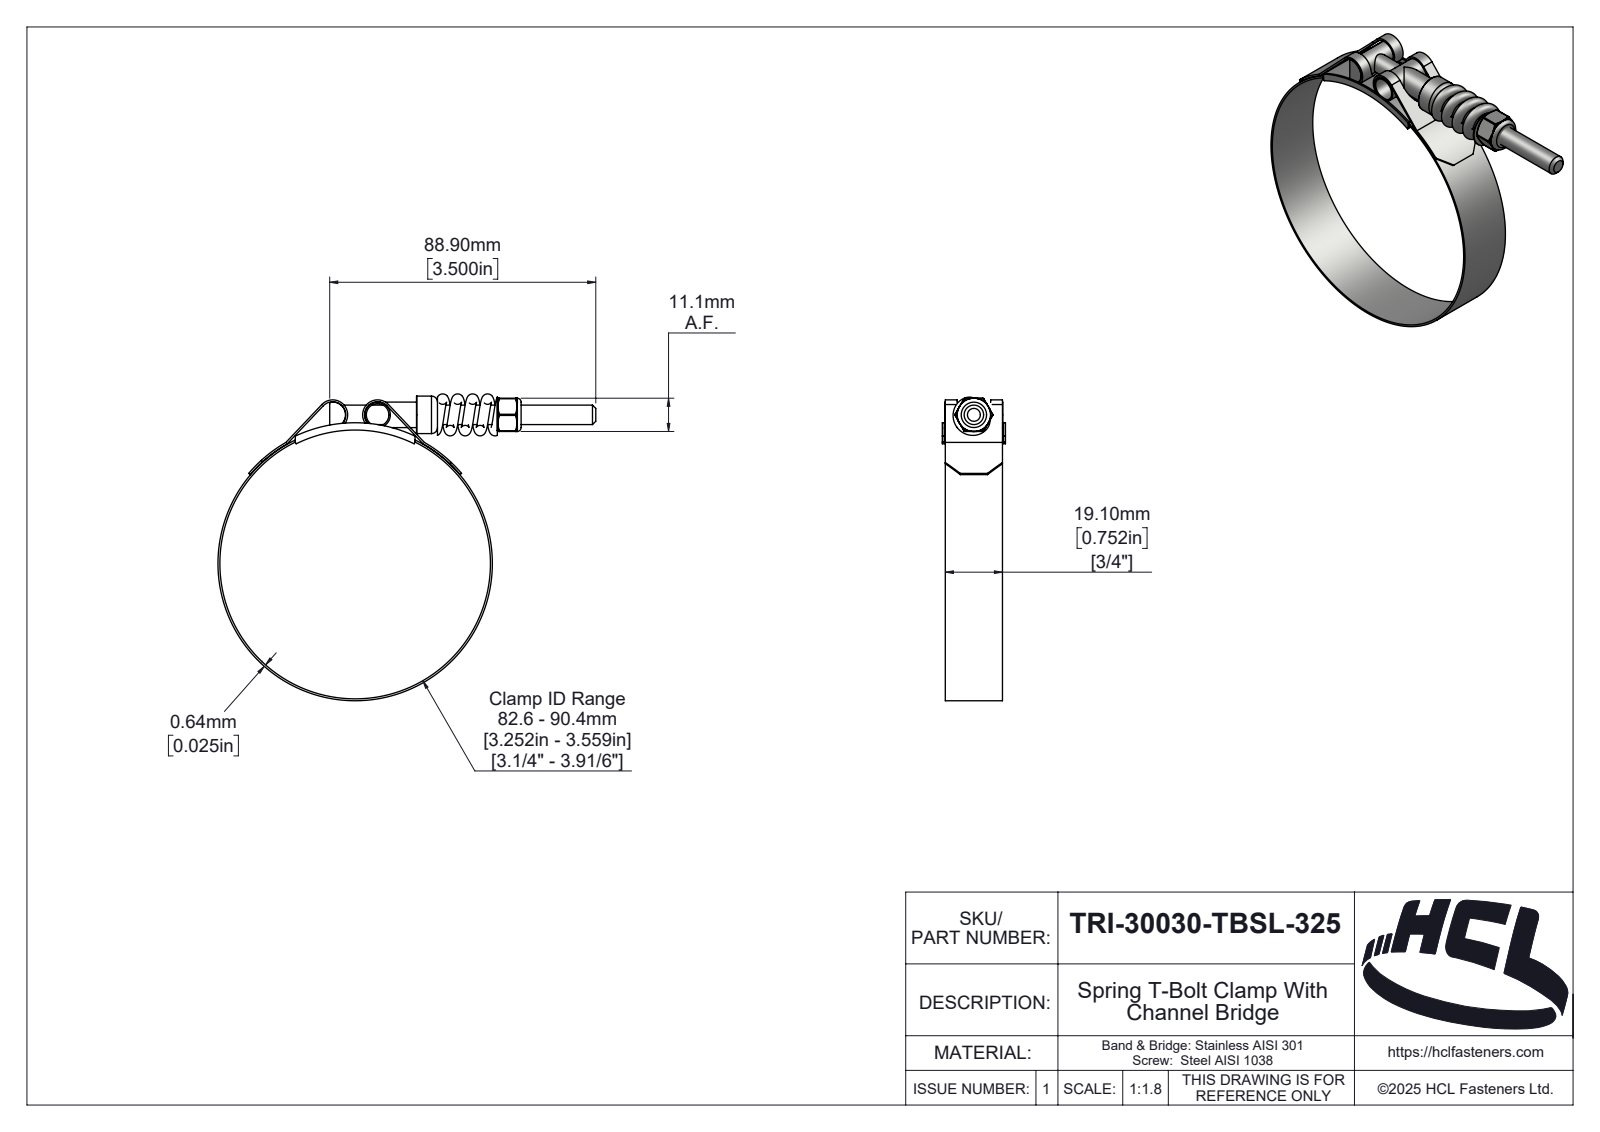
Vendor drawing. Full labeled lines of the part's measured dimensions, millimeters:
Part name (STEP PRODUCT): TRI-30030-TBSL-325
STEP written by: SolidWorks 2025 (AUTOMOTIVE_DESIGN)
Units: millimetres
Bodies: 7 solids, 332 faces (48 planar, 122 cylindrical, 162 other)
Overall size (bounding box): 127.24 × 102.5 × 21.1
Volume: 11 313 mm³ · Surface area: 22 475 mm²
Round holes (diameter × count): ⌀5.4 ×1, ⌀6.35 ×1, ⌀6.5 ×1, ⌀7.52 ×1, ⌀90.4 ×1
Round bosses / shafts (diameter × count): ⌀8.52 ×2, ⌀91.68 ×1, ⌀12.52 ×1
Partial cylindrical surfaces — rounded edges, fillets, slot ends (radius × count): R0.39 ×6, R0.5 ×2, R4.36 ×2, R5 ×2, R0.59 ×1, R2.42 ×1, R3.03 ×1, R3.19 ×1
Main face-to-face distances: 0.64, 19.1, 1, 20.1, 20.46, 0.36, 19.46, 56, 11.11, 21.1
Hole centre spacings: 50.2
